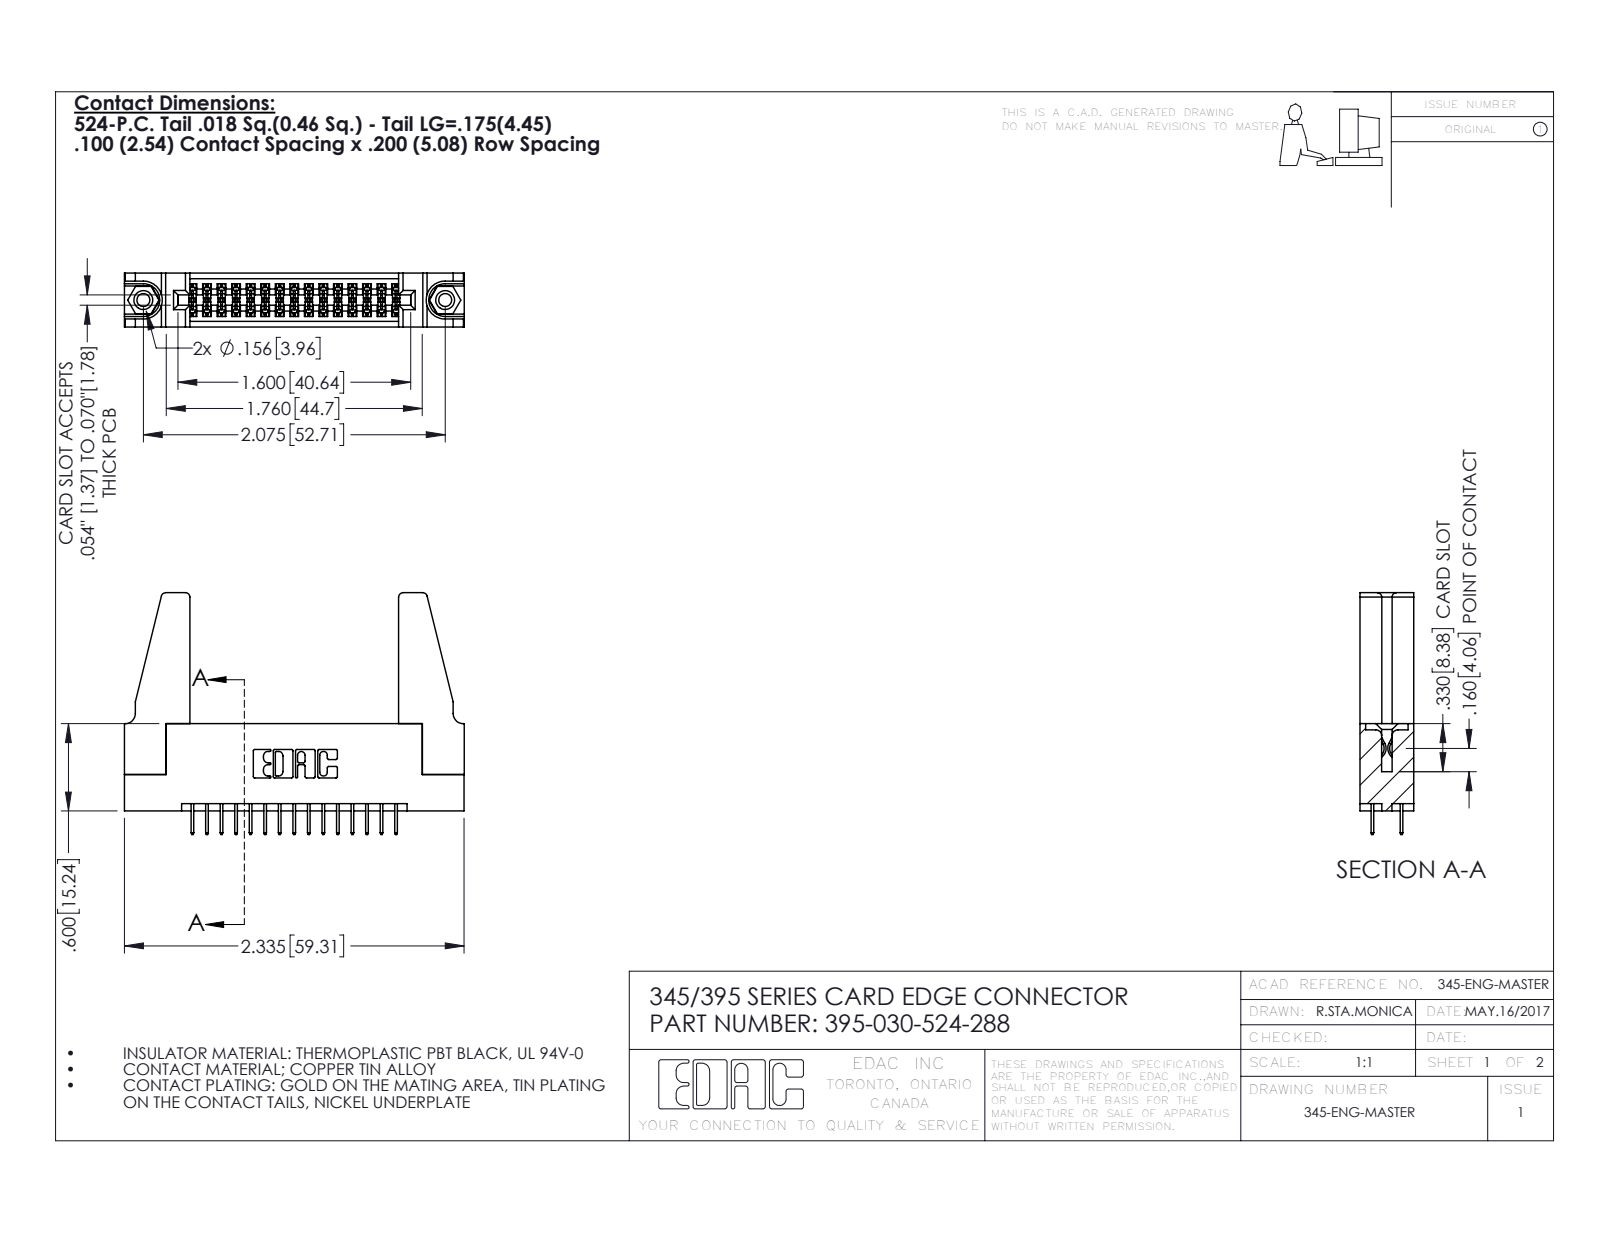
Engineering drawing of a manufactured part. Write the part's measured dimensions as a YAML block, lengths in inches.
part_name: "345-292-001_345-293-124; 345-250-001_345-250-001-102; 395-030-524-288; 345 Part_Flush Mounting Lugs - 0.156 Dia-TH (+1 more)"
step_written_by: "SolidWorks 2016 (CONFIG_CONTROL_DESIGN)"
units: inches
bodies: {solids: 35, faces: 1870, planar: 1322, cylindrical: 532, other: 16}
overall_size: [2.336, 1.662, 0.37]
volume: 0.532
surface_area: 16.37
round_holes:
  - {diameter: 0.089, count: 2}
  - {diameter: 0.125, count: 2}
  - {diameter: 0.156, count: 2}
  - {diameter: 0.064, count: 1}
round_bosses_or_shafts:
  - {diameter: 0.155, count: 2}
partial_cylinders:
  - {radius: 0.006, count: 45}
  - {radius: 0.01, count: 22}
  - {radius: 0.03, count: 8}
  - {radius: 0.007, count: 6}
  - {radius: 0.031, count: 6}
  - {radius: 0.026, count: 3}
  - {radius: 0.014, count: 2}
  - {radius: 0.019, count: 2}
face_to_face_distances: [0.37, 0.072, 0.298, 0.2, 0.098, 0.272, 0.025, 0.225, 0.148, 0.15]
hole_center_spacings: [0.27, 1.842, 2.075]
